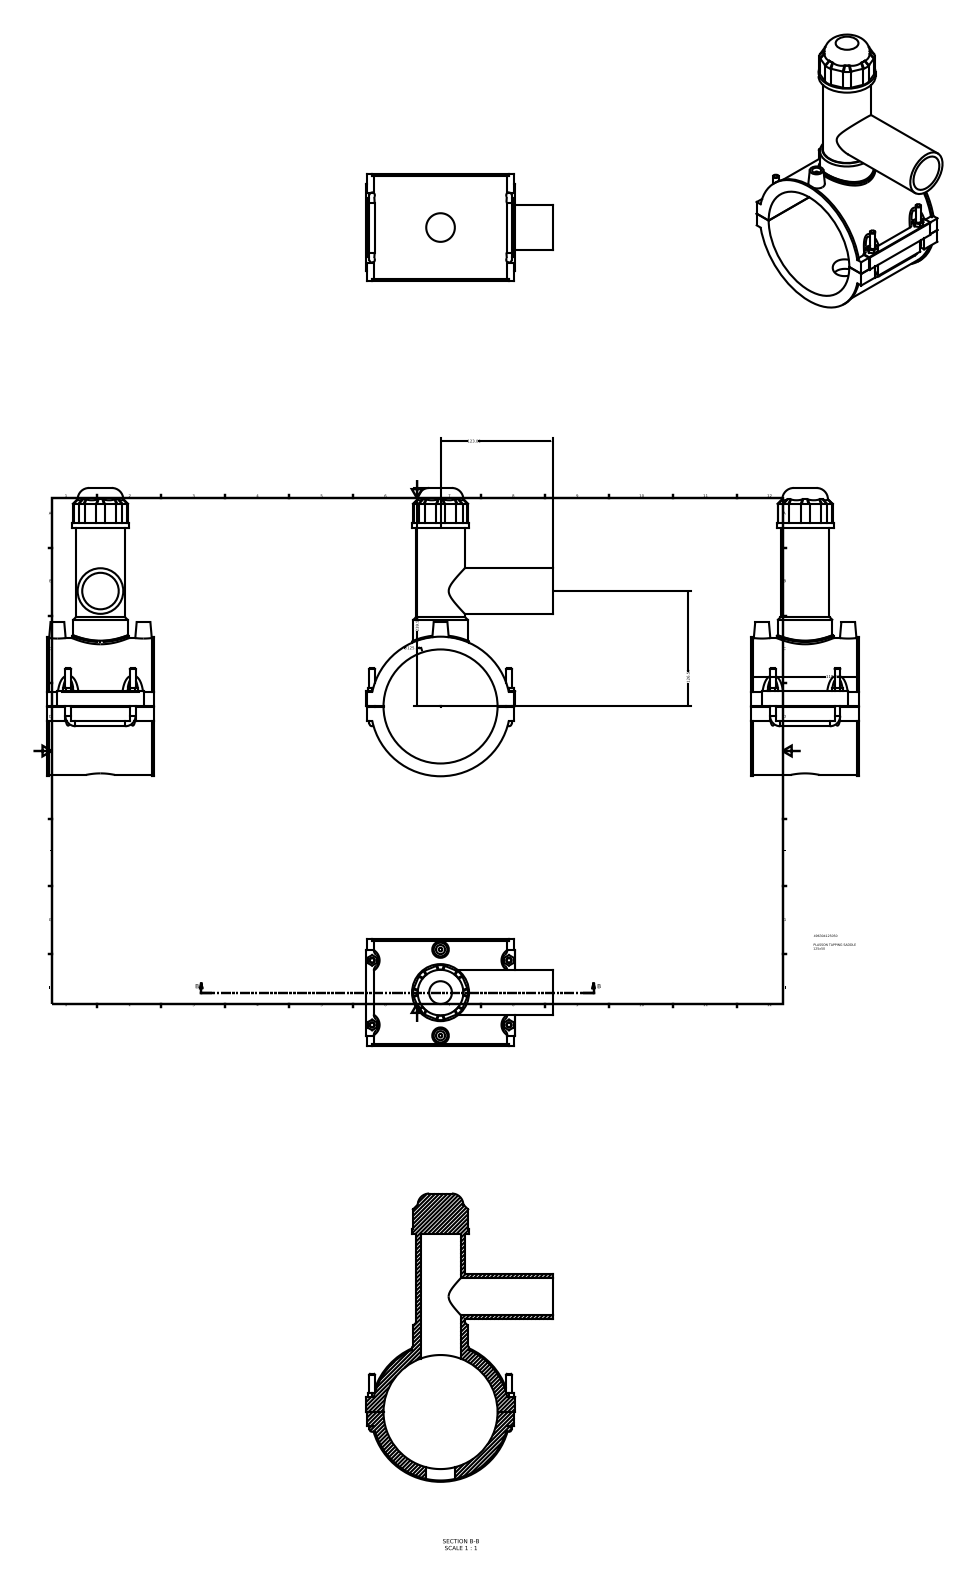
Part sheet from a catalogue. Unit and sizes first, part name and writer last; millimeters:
Units: millimetres
Overall size (bounding box): 316 × 205 × 118
Round holes (diameter × count): ⌀10 ×2, ⌀31.36 ×1, ⌀40 ×1, ⌀43.75 ×1, ⌀125 ×1
Round bosses / shafts (diameter × count): ⌀6 ×4, ⌀4 ×2, ⌀153 ×1, ⌀150 ×1, ⌀62.5 ×1, ⌀59.38 ×1, ⌀53.12 ×1, ⌀50 ×1
Partial cylindrical surfaces — rounded edges, fillets, slot ends (radius × count): R12.5 ×8, R3 ×6, R7.5 ×4, R0.5 ×1, R78 ×1
Main face-to-face distances: 118, 1, 163, 195.3, 195.2, 162, 15.57, 15.67, 210.87, 32.25
Hole centre spacings: 47.2, 94.4
Volume: 947 045 mm³ · Surface area: 210 724 mm²
Bodies: 1 solid, 227 faces (126 planar, 56 cylindrical, 45 other)
Part name (STEP PRODUCT): 496304125050
STEP written by: Autodesk Inventor 2015 (AUTOMOTIVE_DESIGN)
